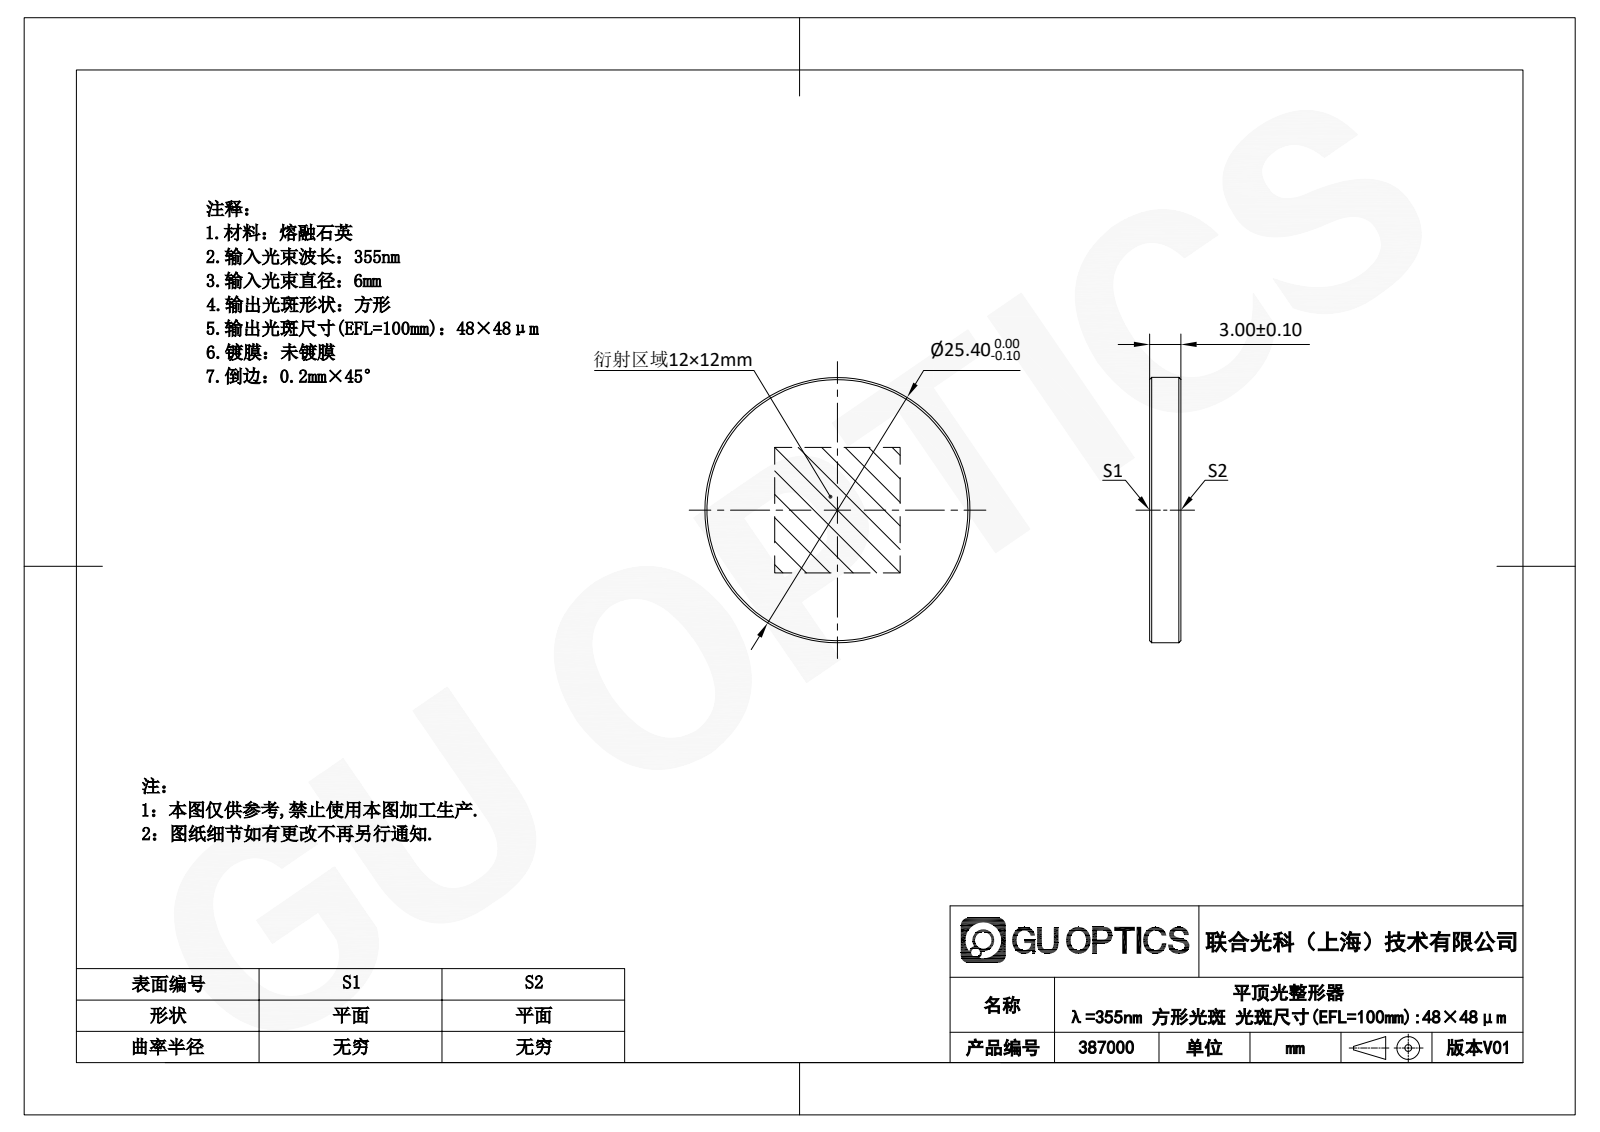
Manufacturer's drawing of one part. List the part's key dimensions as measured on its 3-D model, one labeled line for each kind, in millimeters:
Part name (STEP PRODUCT): 25.4
STEP written by: SolidWorks 2020 (CONFIG_CONTROL_DESIGN)
Units: millimetres
Bodies: 1 solid, 5 faces (2 planar, 1 cylindrical, 2 other)
Overall size (bounding box): 25.4 × 25.4 × 3
Volume: 1 517 mm³ · Surface area: 1 234 mm²
Round bosses / shafts (diameter × count): ⌀25.4 ×1
Main face-to-face distances: 3
